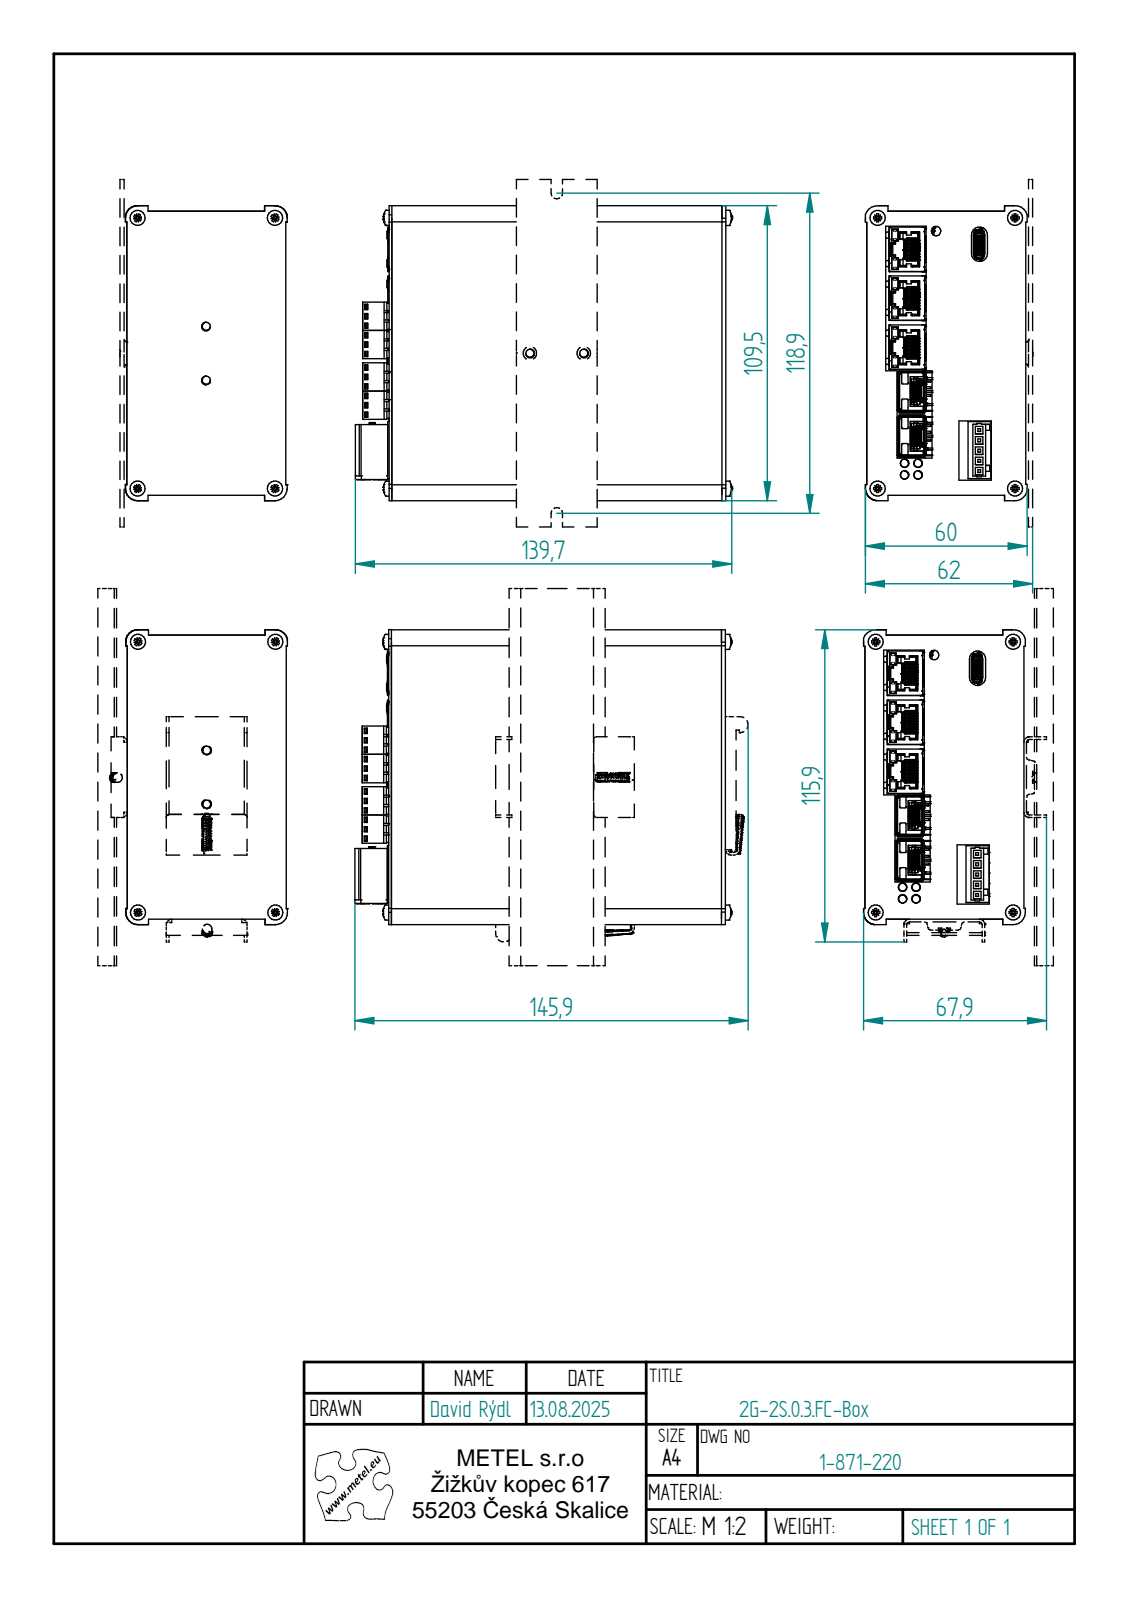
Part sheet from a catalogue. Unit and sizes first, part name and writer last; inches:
Units: inches
Overall size (bounding box): 5.745 × 5.512 × 2.772
Round holes (diameter × count): ⌀0.118 ×10, ⌀0.138 ×7, ⌀0.139 ×6, ⌀0.059 ×5, ⌀0.018 ×4, ⌀0.126 ×4, ⌀0.134 ×4, ⌀0.016 ×2, ⌀0.02 ×2, ⌀0.157 ×2
Round bosses / shafts (diameter × count): ⌀0.22 ×4, ⌀0.118 ×4, ⌀0.114 ×4, ⌀0.079 ×3, ⌀0.071 ×2, ⌀0.07 ×2, ⌀0.024 ×2, ⌀0.018 ×2
Partial cylindrical surfaces — rounded edges, fillets, slot ends (radius × count): R0.004 ×148, R0.01 ×141, R0.008 ×91, R0.006 ×83, R0.01 ×78, R0.009 ×54, R0.039 ×50, R0.04 ×48
Main face-to-face distances: 0.059, 2.264, 0.039, 0.157, 2.323, 0.098, 3.996, 2.205, 2.362, 3.839
Hole centre spacings: 0.15, 1.876, 2.576, 0.22, 0.3, 0.787, 0.039, 0.044
Volume: 9.007 in³ · Surface area: 271.6 in²
Bodies: 50 solids, 12752 faces (9244 planar, 2870 cylindrical, 638 other)
Part name (STEP PRODUCT): 2G-2S.0.3.FC_zakaznik; profil_velky_prekresleny_zakaznik; 2G-2S.0.3.FC; Zadni panylek_velky (+8 more)
STEP written by: Solid Edge (AUTOMOTIVE_DESIGN)
